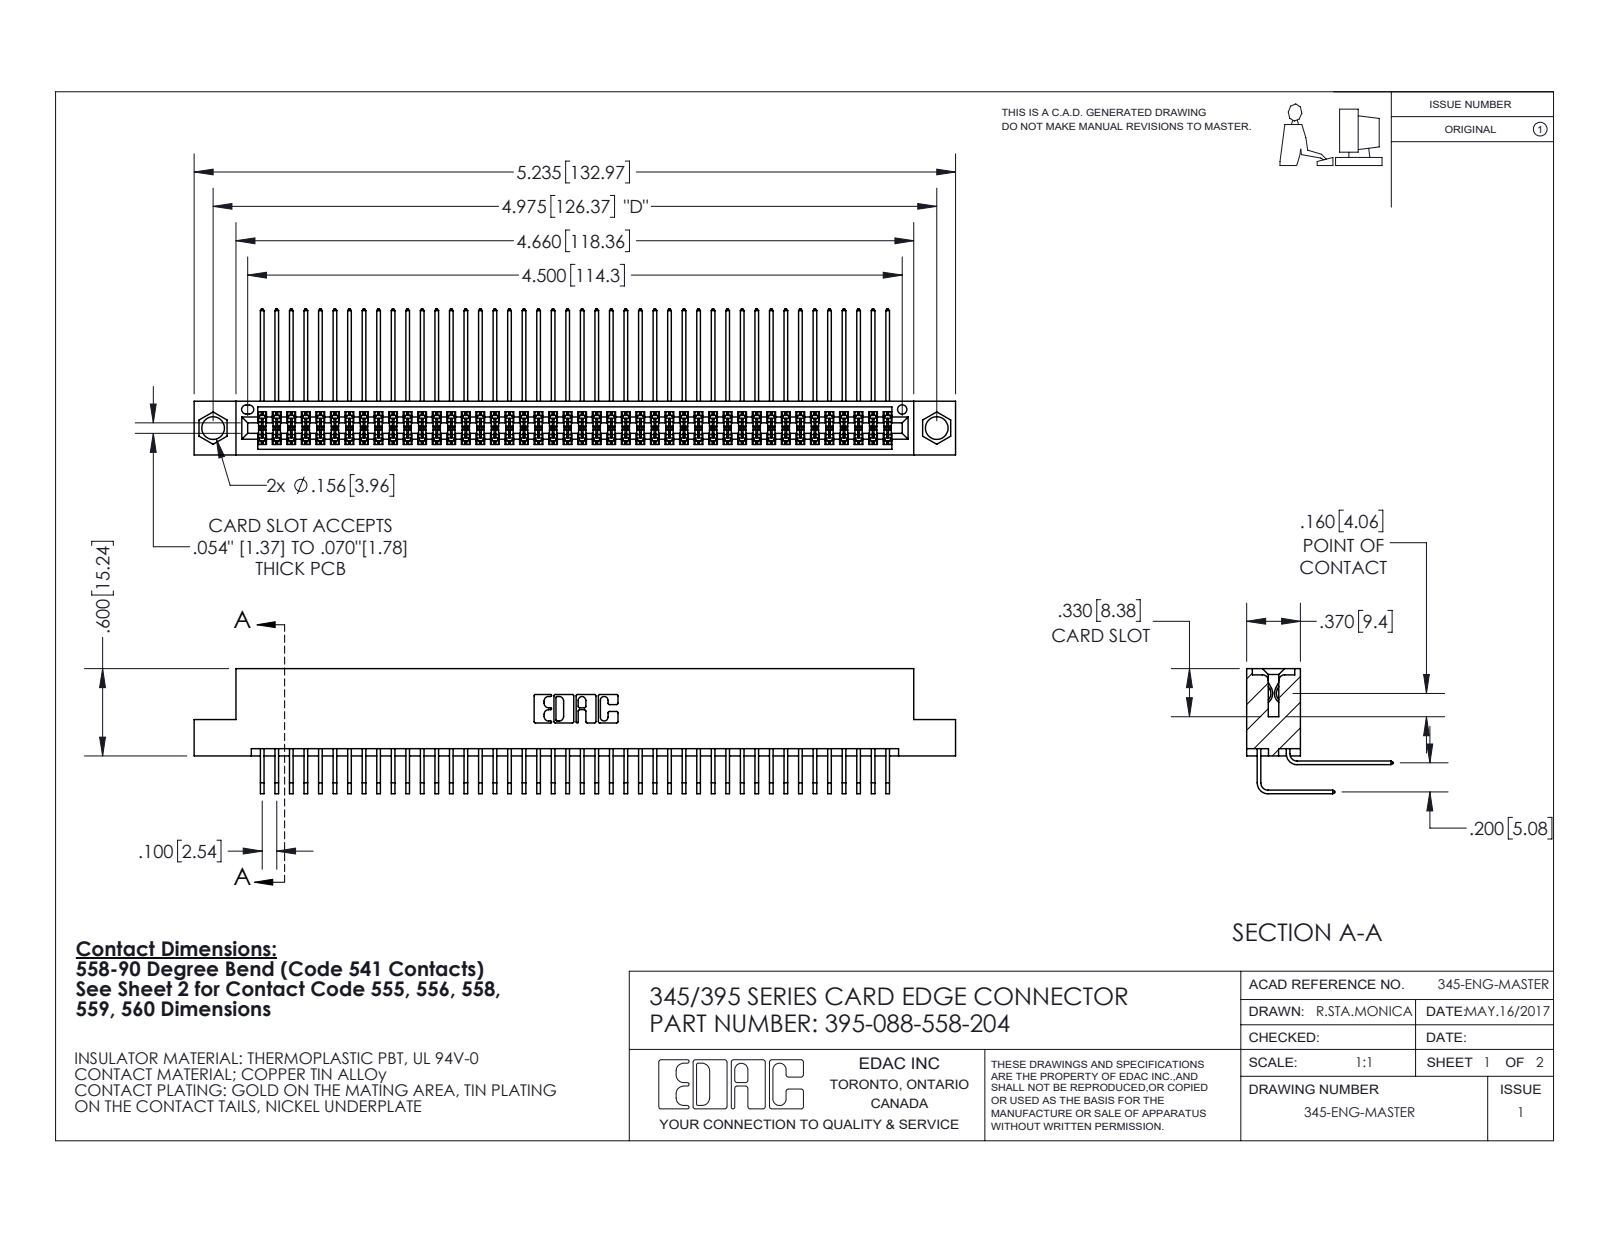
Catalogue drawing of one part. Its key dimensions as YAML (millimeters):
part_name: "345 Part_Flush Mounting Lugs - 0.156 Dia-TI; 345-292-001_558 559 Tail - 1; 395-088-558-204; 345-292-001_558 Tail - 2"
step_written_by: "SolidWorks 2020 (CONFIG_CONTROL_DESIGN)"
units: millimeters
bodies: {solids: 89, faces: 4716, planar: 3174, cylindrical: 1542, other: 0}
overall_size: [133, 25.5, 21.8]
volume: 13300
surface_area: 21990
round_holes:
  - {diameter: 4, count: 2}
  - {diameter: 1.6, count: 1}
partial_cylinders:
  - {radius: 0.2, count: 176}
  - {radius: 0.3, count: 22}
  - {radius: 0.2, count: 6}
  - {radius: 0.8, count: 6}
  - {radius: 0.7, count: 3}
  - {radius: 0.4, count: 2}
  - {radius: 0.5, count: 2}
  - {radius: 0.6, count: 2}
face_to_face_distances: [1.8, 7.6, 5.1, 9.4, 2.5, 6.9, 0.6, 5.7, 0.6, 4.4]
hole_center_spacings: [6.9, 120.4, 126.4]
